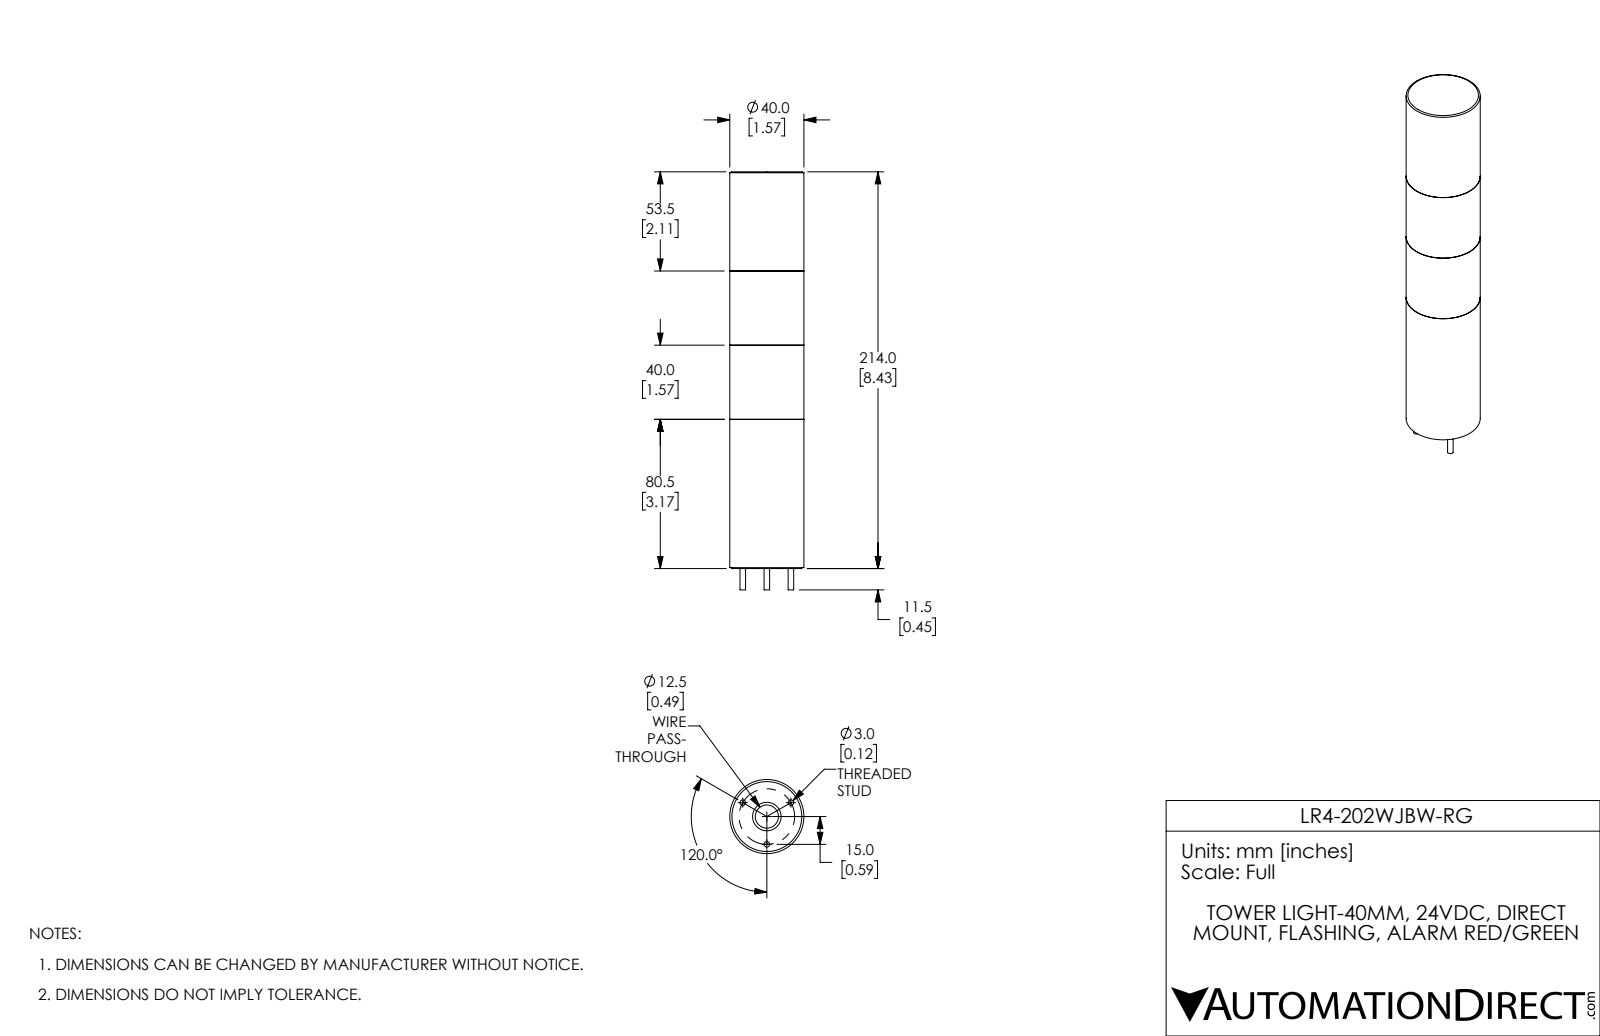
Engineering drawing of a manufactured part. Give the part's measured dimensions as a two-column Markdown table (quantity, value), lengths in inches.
| quantity | value |
| --- | --- |
| part name | LR4-202WJBW-RG |
| STEP written by | SolidWorks 2017 (AUTOMOTIVE_DESIGN) |
| units | inches |
| bodies | 4 solids, 69 faces (25 planar, 42 cylindrical, 2 other) |
| overall size | 8.878 × 1.575 × 1.575 |
| volume | 16.29 in³ |
| surface area | 68.9 in² |
| round holes (diameter × count) | 0.492 × 1, 0.606 × 1, 1.386 × 1, 1.463 × 1, 1.476 × 1 |
| round bosses / shafts (diameter × count) | 0.118 × 3, 1.575 × 1, 1.484 × 1, 1.461 × 1, 1.366 × 1 |
| main face-to-face distances | 1.575, 3.15, 3.276, 4.85, 1.701, 3.161, 1.587, 1.689, 0.406, 3.575 |
